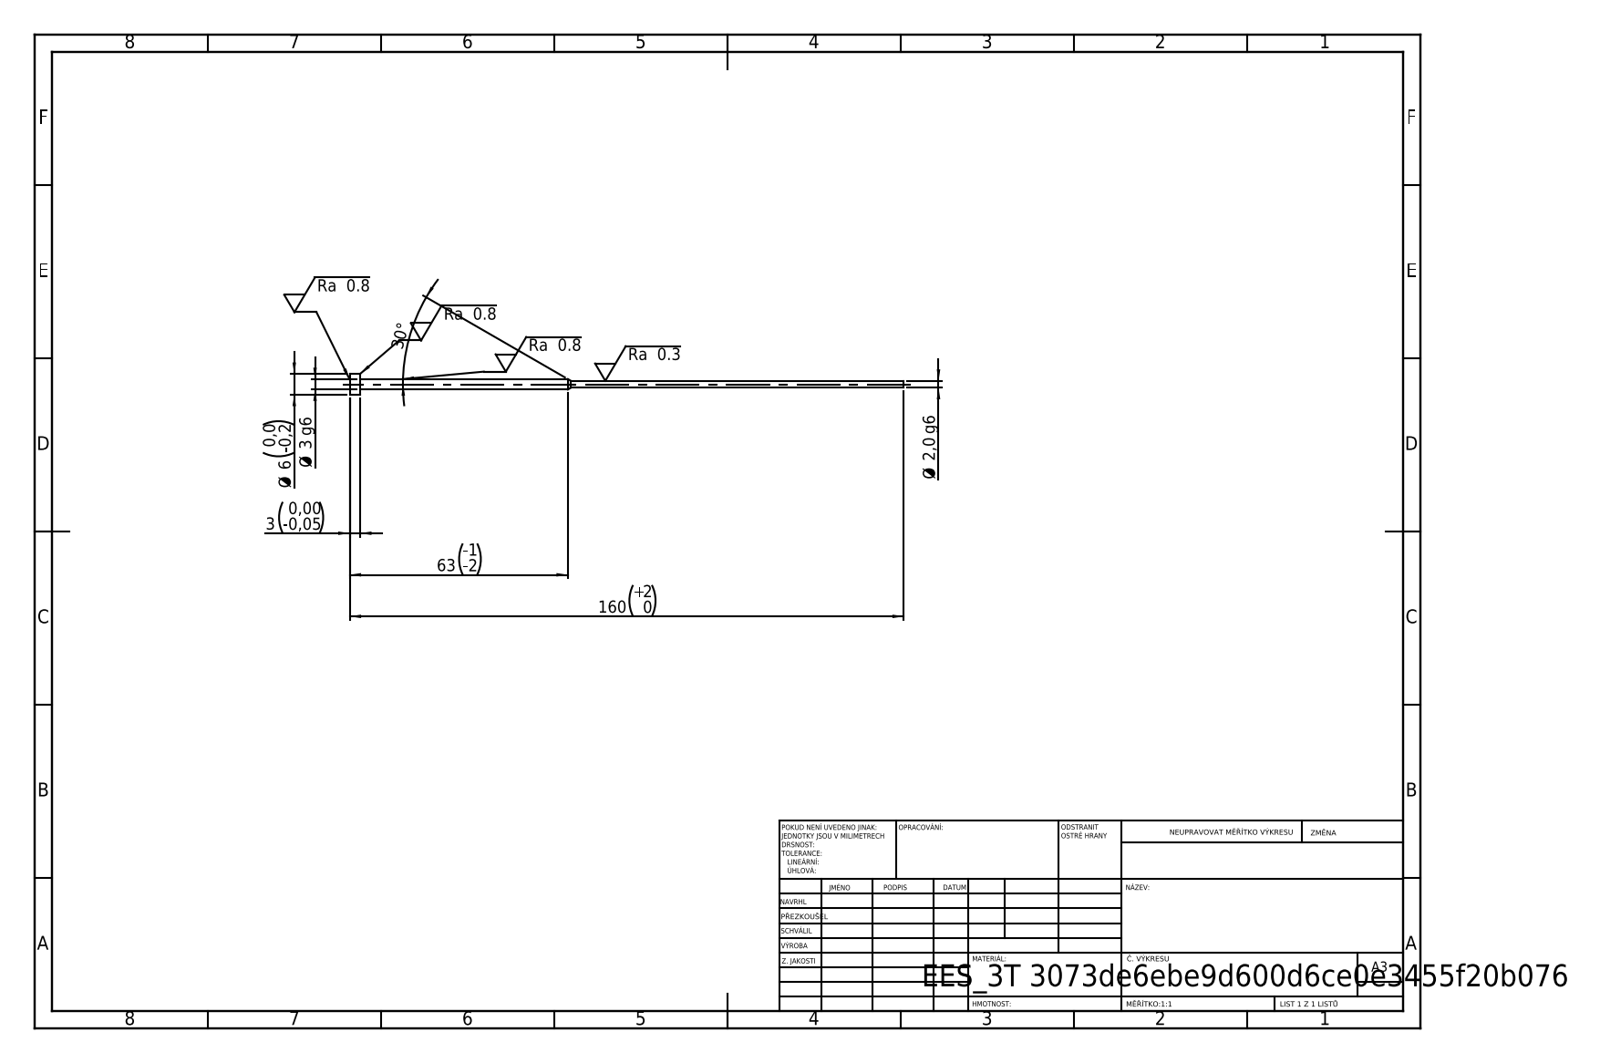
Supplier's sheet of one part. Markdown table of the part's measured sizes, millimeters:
| quantity | value |
| --- | --- |
| STEP written by | SolidWorks 2019 (CONFIG_CONTROL_DESIGN) |
| units | millimeters |
| bodies | 1 solid, 11 faces (3 planar, 6 cylindrical, 2 other) |
| overall size | 160 × 6 × 6 |
| volume | 815 mm³ |
| surface area | 1 287 mm² |
| round bosses / shafts (diameter × count) | 6 × 1, 3 × 1, 2 × 1 |
| main face-to-face distances | 3, 157, 160 |
